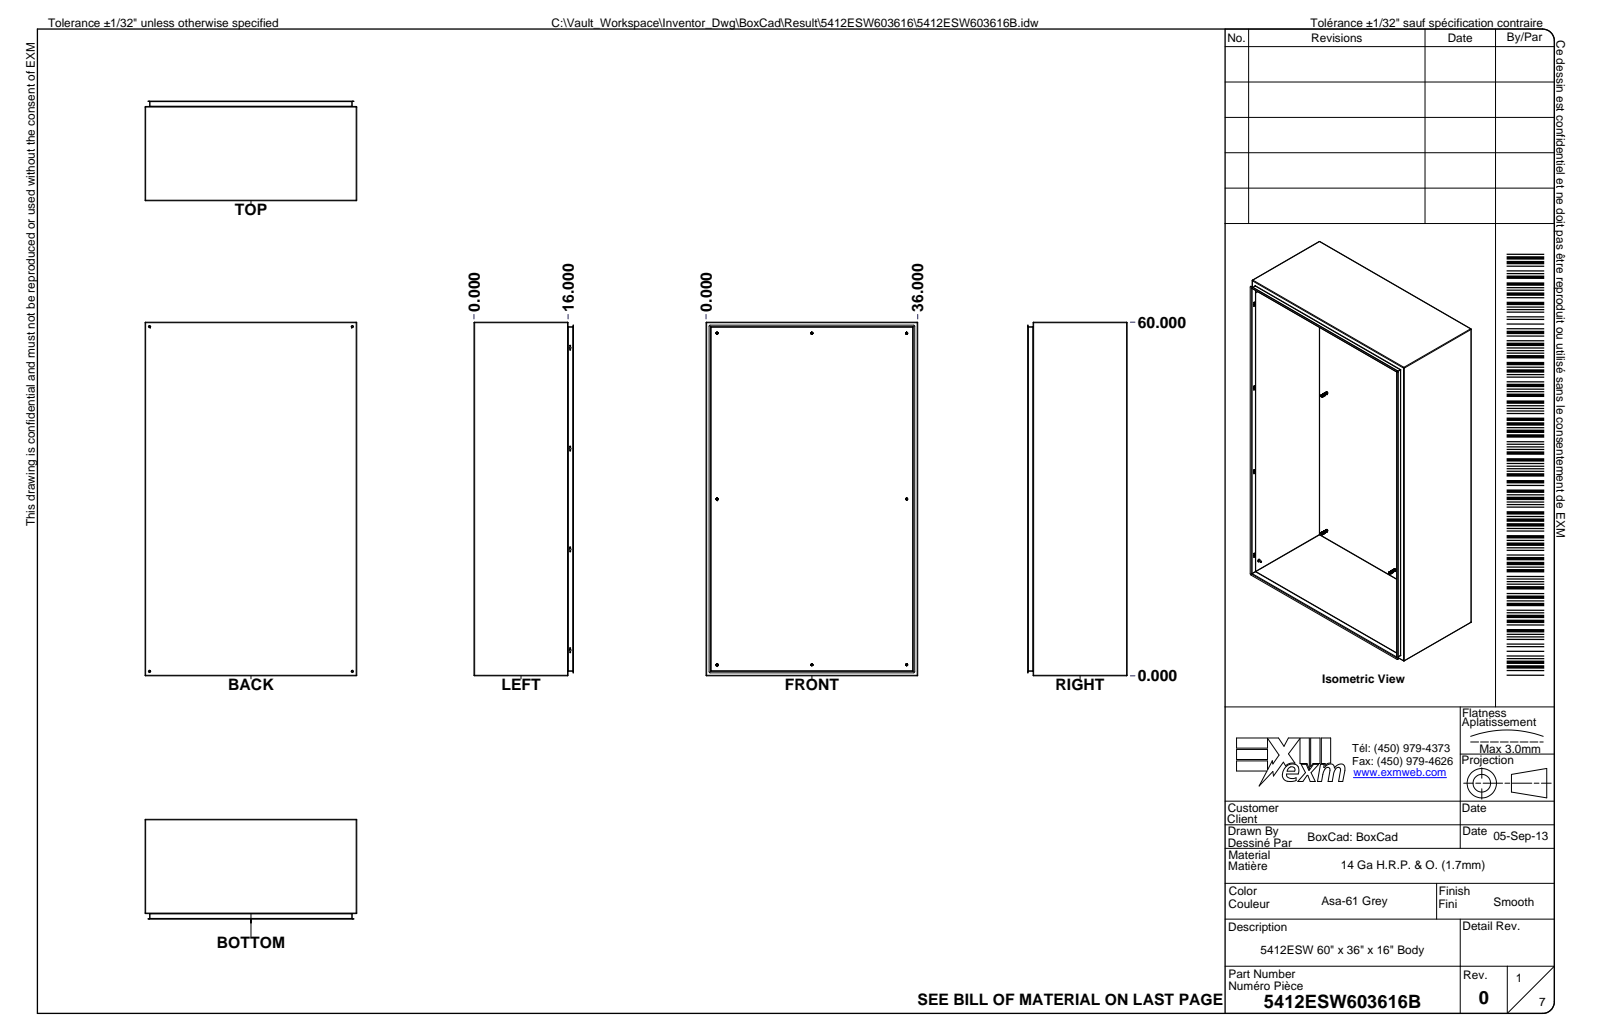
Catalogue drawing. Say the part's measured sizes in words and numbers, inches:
The part is named "5412ESW603616; 5412ESW603616B; 5412ESW603616B-P; STK-Q-16005 (+8 more)". Its 3-D file was written by "Autodesk Inventor 2024 (AUTOMOTIVE_DESIGN)". It is 185 solids with 29258 faces: 12835 planar, 6480 cylindrical and 9943 other. Overall it measures 60 by 36.018 by 17.295 inches. Its volume is 1 152 cubic inches and its surface area 21 344 square inches. Round holes: 34 of diameter 0.03, 32 of diameter 0.315, 31 of diameter 0.201, 28 of diameter 0.29, 24 of diameter 0.197, 24 of diameter 0.276, 24 of diameter 0.374, 16 of diameter 0.043, 8 of diameter 0.173, 8 of diameter 0.178, 8 of diameter 0.27, 4 of diameter 0.187. Round bosses or shafts: 33 of diameter 0.03, 32 of diameter 0.232, 24 of diameter 0.354, 16 of diameter 0.039, 8 of diameter 0.717, 8 of diameter 0.311, 8 of diameter 0.271, 8 of diameter 0.262. Partial cylindrical surfaces (rounded edges, fillets, slot ends): 625 of radius 0.02, 231 of radius 0.01, 204 of radius 0.039, 170 of radius 0.008, 170 of radius 0.031, 128 of radius 0.086, 106 of radius 0.016, 74 of radius 0.012. The main face-to-face distances are 0.068, 0.942, 0.874, 1.047, 0.979, 0.105, 35.932, 16.744, 16.676, 15.802. The hole center spacings are 32.776, 17.101, 34.202, 35.003, 0.35, 0.735, 1.052, 1.385.
